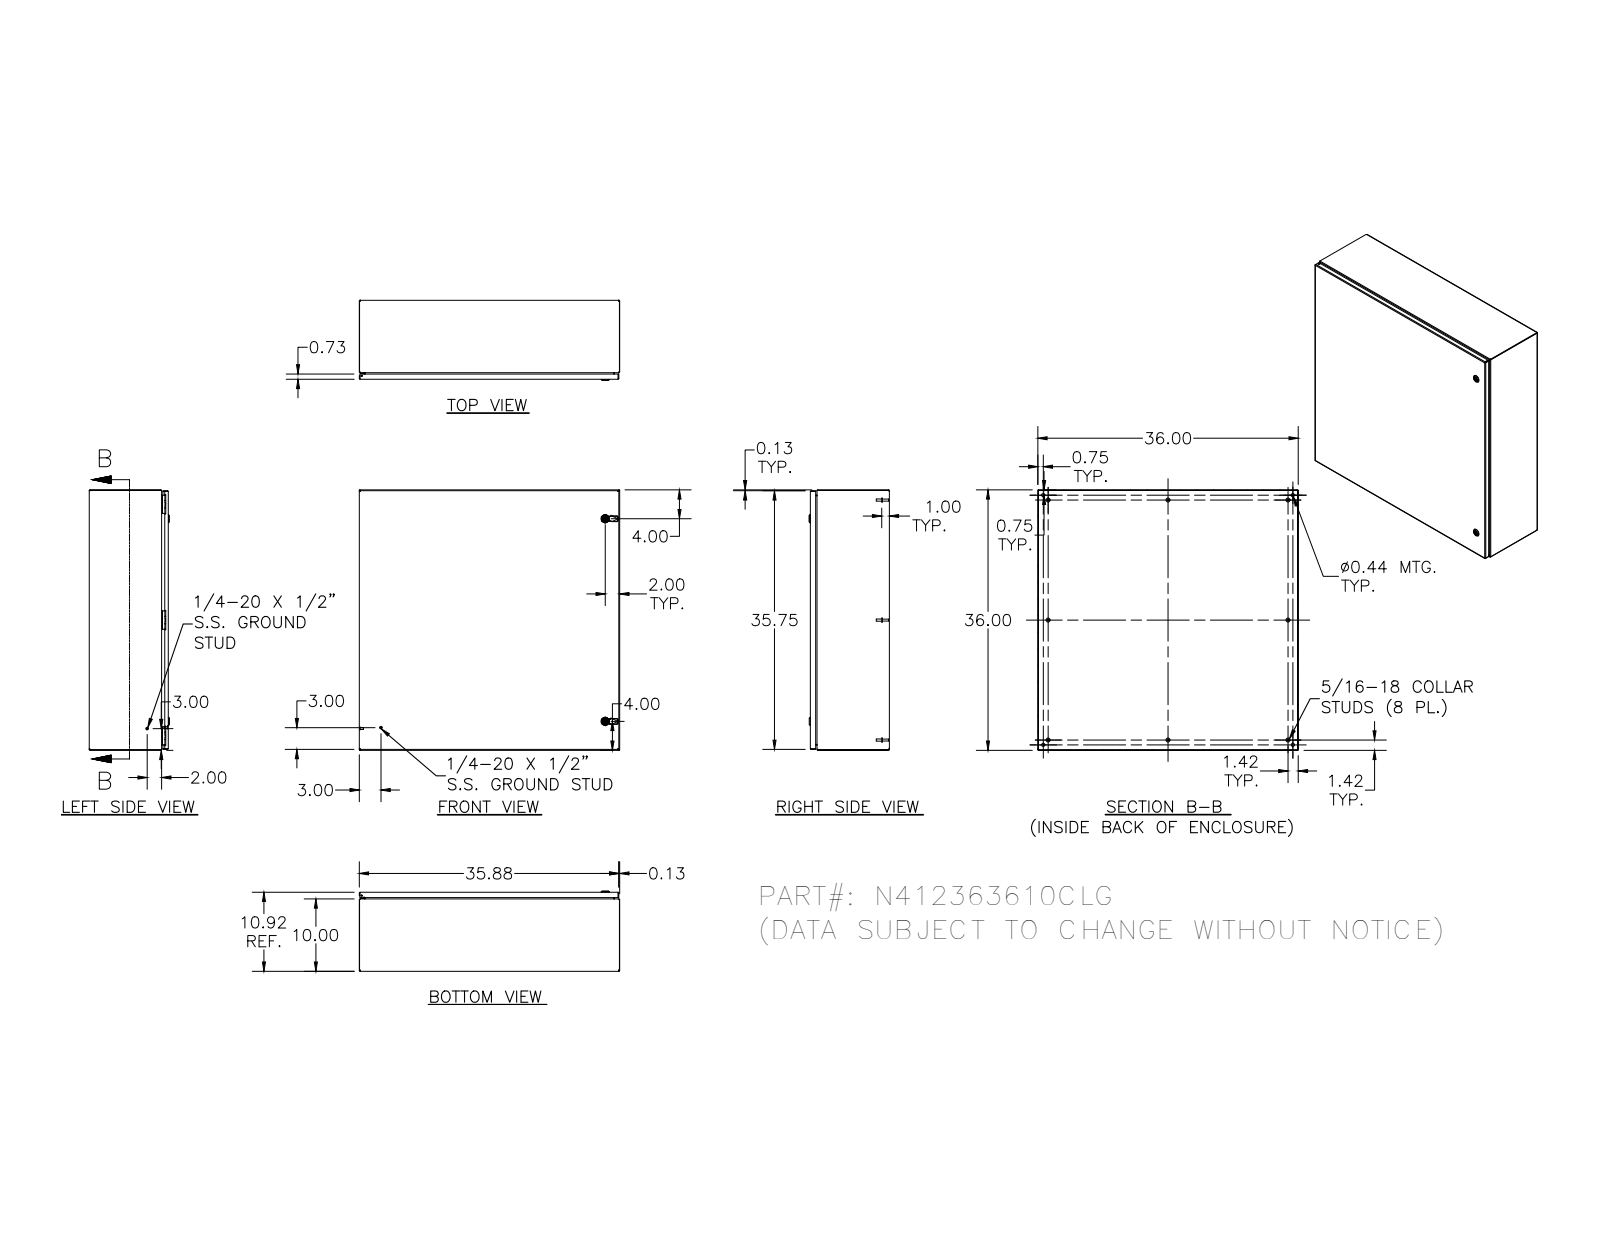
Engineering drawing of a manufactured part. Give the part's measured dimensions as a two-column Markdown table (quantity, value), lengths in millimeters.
| quantity | value |
| --- | --- |
| part name | N412363610C; N4123636CLID; 35124; 1000-u155_asm (+8 more) |
| STEP written by | Autodesk Inventor 2011 (AUTOMOTIVE_DESIGN) |
| units | millimeters |
| bodies | 51 solids, 2268 faces (839 planar, 862 cylindrical, 567 other) |
| overall size | 914.4 × 914.4 × 281.3 |
| volume | 5 244 000 mm³ |
| surface area | 5 608 000 mm² |
| round holes (diameter × count) | 4.8 × 7, 2.4 × 6, 3.9 × 6, 4.2 × 6, 4.4 × 6, 11.1 × 4, 4 × 3, 5 × 2, 8 × 2, 10 × 2, 10.2 × 2, 16.1 × 2 |
| round bosses / shafts (diameter × count) | 6.4 × 14, 14.3 × 8, 7.6 × 8, 7 × 8, 9.1 × 6, 8.1 × 6, 6.5 × 6, 4.2 × 6 |
| partial cylindrical surfaces (radius × count) | 0.3 × 54, 1.3 × 38, 0.8 × 34, 0.4 × 26, 3.2 × 24, 0.5 × 23, 2.7 × 20, 0.8 × 12 |
| main face-to-face distances | 1.9, 275.4, 273.5, 277.3, 1.9, 912.5, 910.6, 912.5, 914.4, 23.3 |
| hole center spacings | 406.4, 812.8, 16.8, 16.7, 33.2, 49.9, 406.6, 876.3 |
